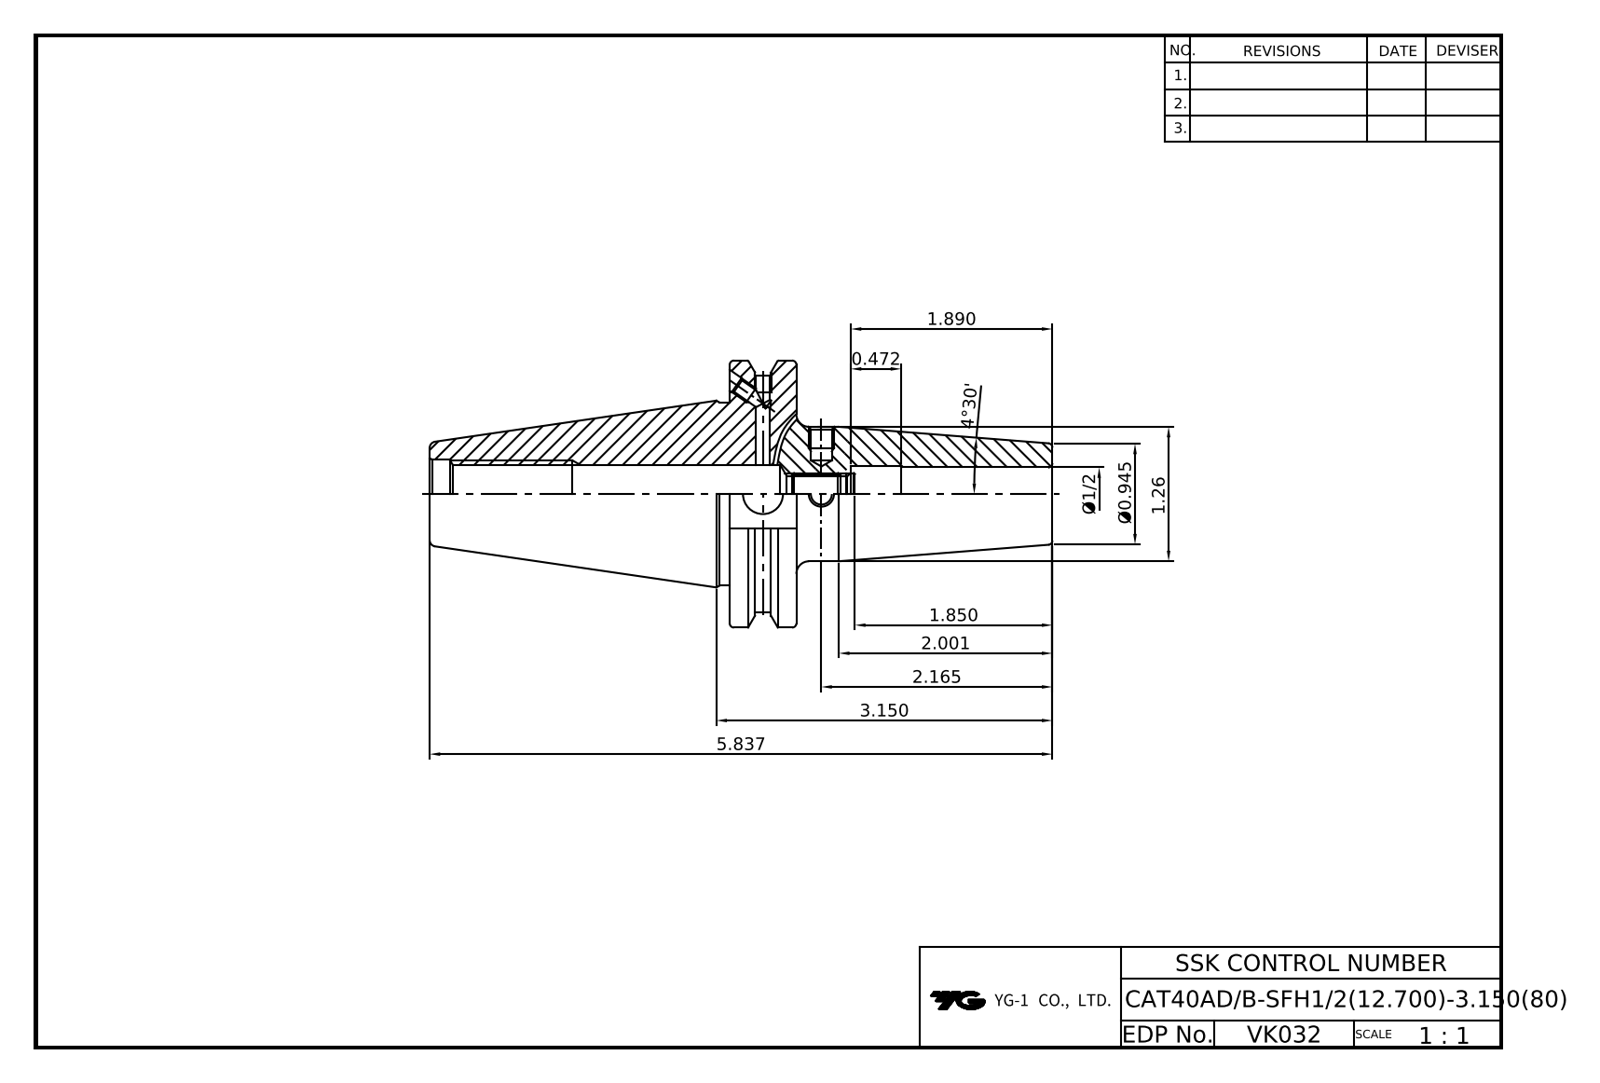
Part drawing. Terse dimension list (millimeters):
name: LO-CAT40ADB-SFH12.7-80
written by: Autodesk Inventor 2024 (AUTOMOTIVE_DESIGN)
unit: mm
bodies: 1 solid, 88 faces (37 planar, 29 cylindrical, 22 other)
size: 148.25 × 63.5 × 61.09
volume: 133 551 mm³; area: 28 130 mm²
holes: 4× ⌀3.24, 2× ⌀4, 2× ⌀4.2, 1× ⌀8.92, 1× ⌀9.53, 1× ⌀12.7, 1× ⌀13, 1× ⌀13.39, 1× ⌀13.9, 1× ⌀16.3
bosses: 1× ⌀63.5, 1× ⌀43.6, 1× ⌀32
rounds: 1× R28.15
face distances: 15.88, 76.83, 60.95, 47.6, 16.38, 71.42, 87.3, 148.25, 77.47, 6.05
